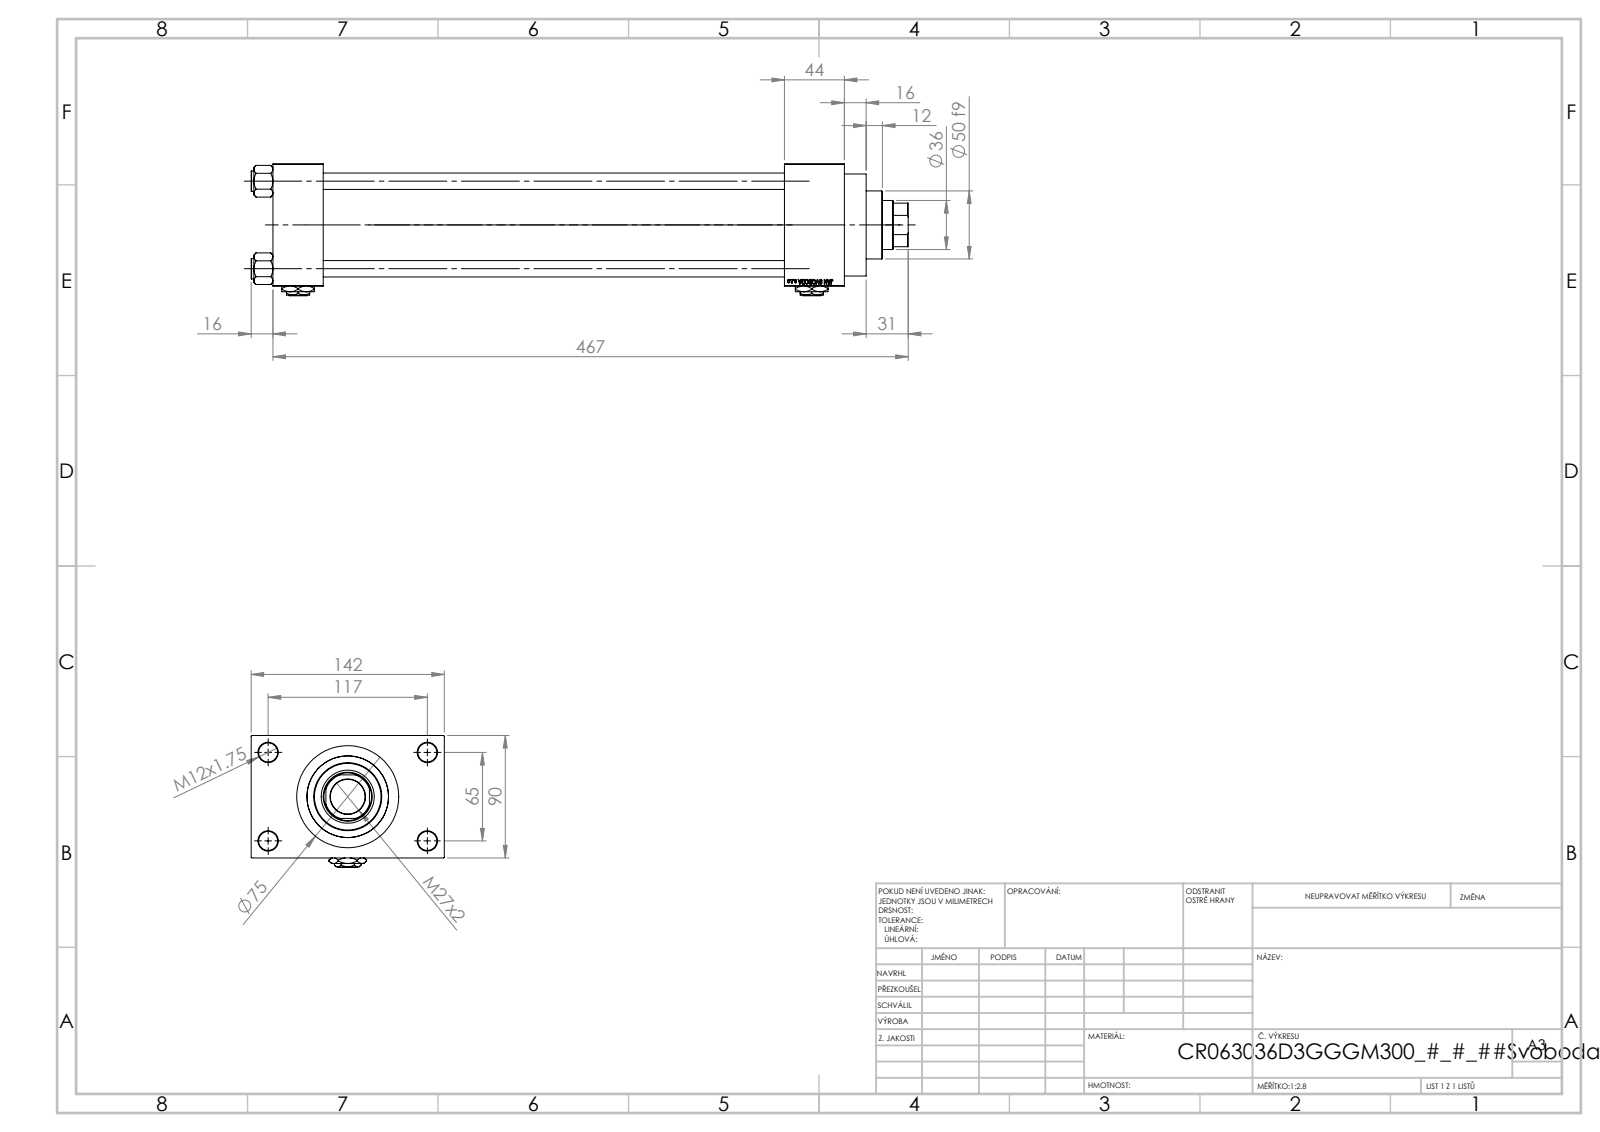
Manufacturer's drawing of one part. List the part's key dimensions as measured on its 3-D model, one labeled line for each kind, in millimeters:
Part name (STEP PRODUCT): NUT_M5_D; V215CR_D_Body; V215CR_VCP_D; V215CR_D_TYCINKA (+2 more)
STEP written by: SolidWorks 2019 (CONFIG_CONTROL_DESIGN)
Units: millimetres
Bodies: 13 solids, 1205 faces (545 planar, 100 cylindrical, 560 other)
Overall size (bounding box): 483 × 142 × 97
Volume: 1 701 000 mm³ · Surface area: 398 710 mm²
Round holes (diameter × count): ⌀12 ×4, ⌀14 ×4, ⌀7 ×2, ⌀20.96 ×2, ⌀30 ×2, ⌀25.5 ×1, ⌀36 ×1, ⌀39 ×1, ⌀50 ×1, ⌀60 ×1, ⌀63 ×1
Round bosses / shafts (diameter × count): ⌀15 ×4, ⌀75 ×1, ⌀69 ×1
Partial cylindrical surfaces — rounded edges, fillets, slot ends (radius × count): R17.5 ×1
Main face-to-face distances: 90, 339, 37, 376, 420, 383, 44, 26, 116, 142
Hole centre spacings: 26.35, 45.47, 64.3, 66.92, 69.81, 90.65, 111.34, 65
